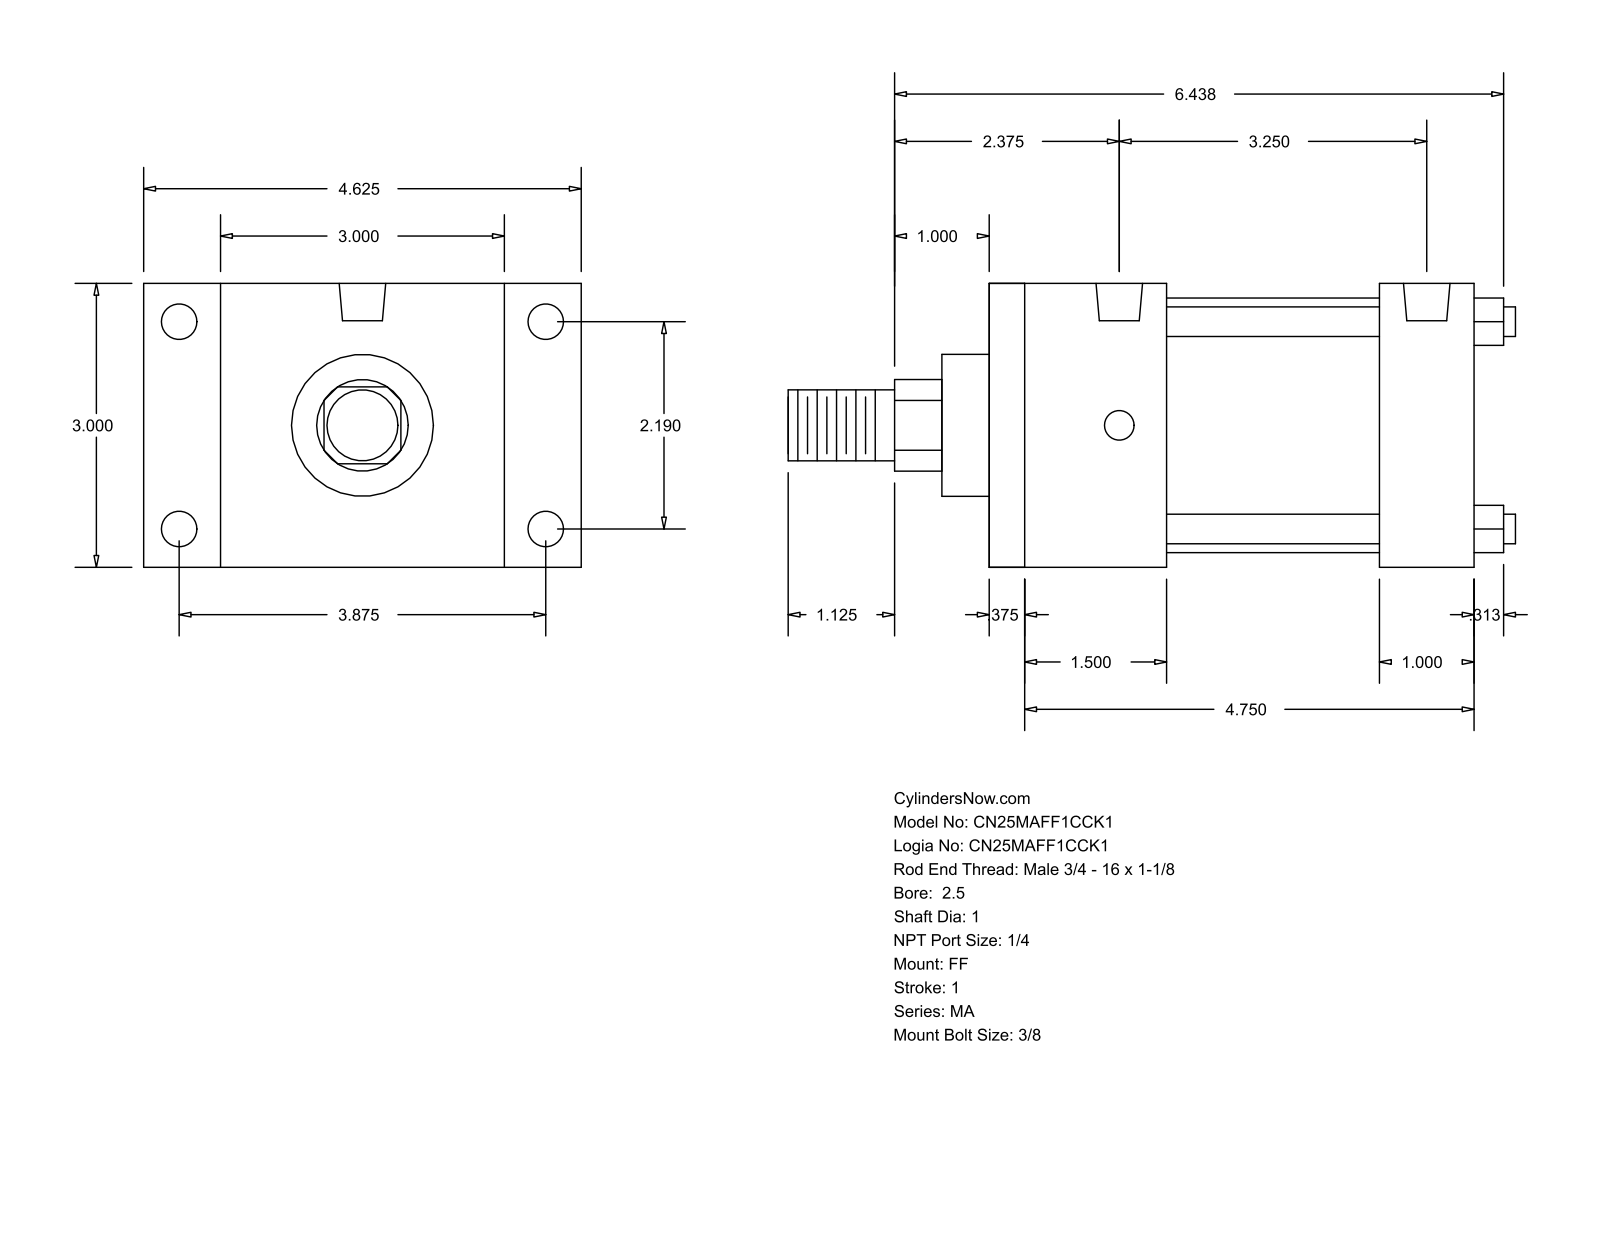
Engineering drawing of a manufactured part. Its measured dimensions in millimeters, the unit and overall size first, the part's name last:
Units: millimetres
Overall size (bounding box): 195.26 × 117.47 × 76.2
Round holes (diameter × count): ⌀7.94 ×4, ⌀9.53 ×4, ⌀12.49 ×2
Round bosses / shafts (diameter × count): ⌀7.94 ×4, ⌀68.33 ×1, ⌀38.1 ×1, ⌀25.4 ×1, ⌀19.05 ×1
Partial cylindrical surfaces — rounded edges, fillets, slot ends (radius × count): R12.29 ×1
Main face-to-face distances: 76.2, 130.17, 120.65, 9.52, 25.39, 47.63, 104.78, 38.11, 95.26, 57.15
Hole centre spacings: 55.62, 82.55, 98.42, 113.05
Bodies: 0 solids, 92 faces (64 planar, 28 cylindrical, 0 other)
Part name (STEP PRODUCT): MA_FF__0250_1
STEP written by: GSSL Pune (CONFIG_CONTROL_DESIGN)
